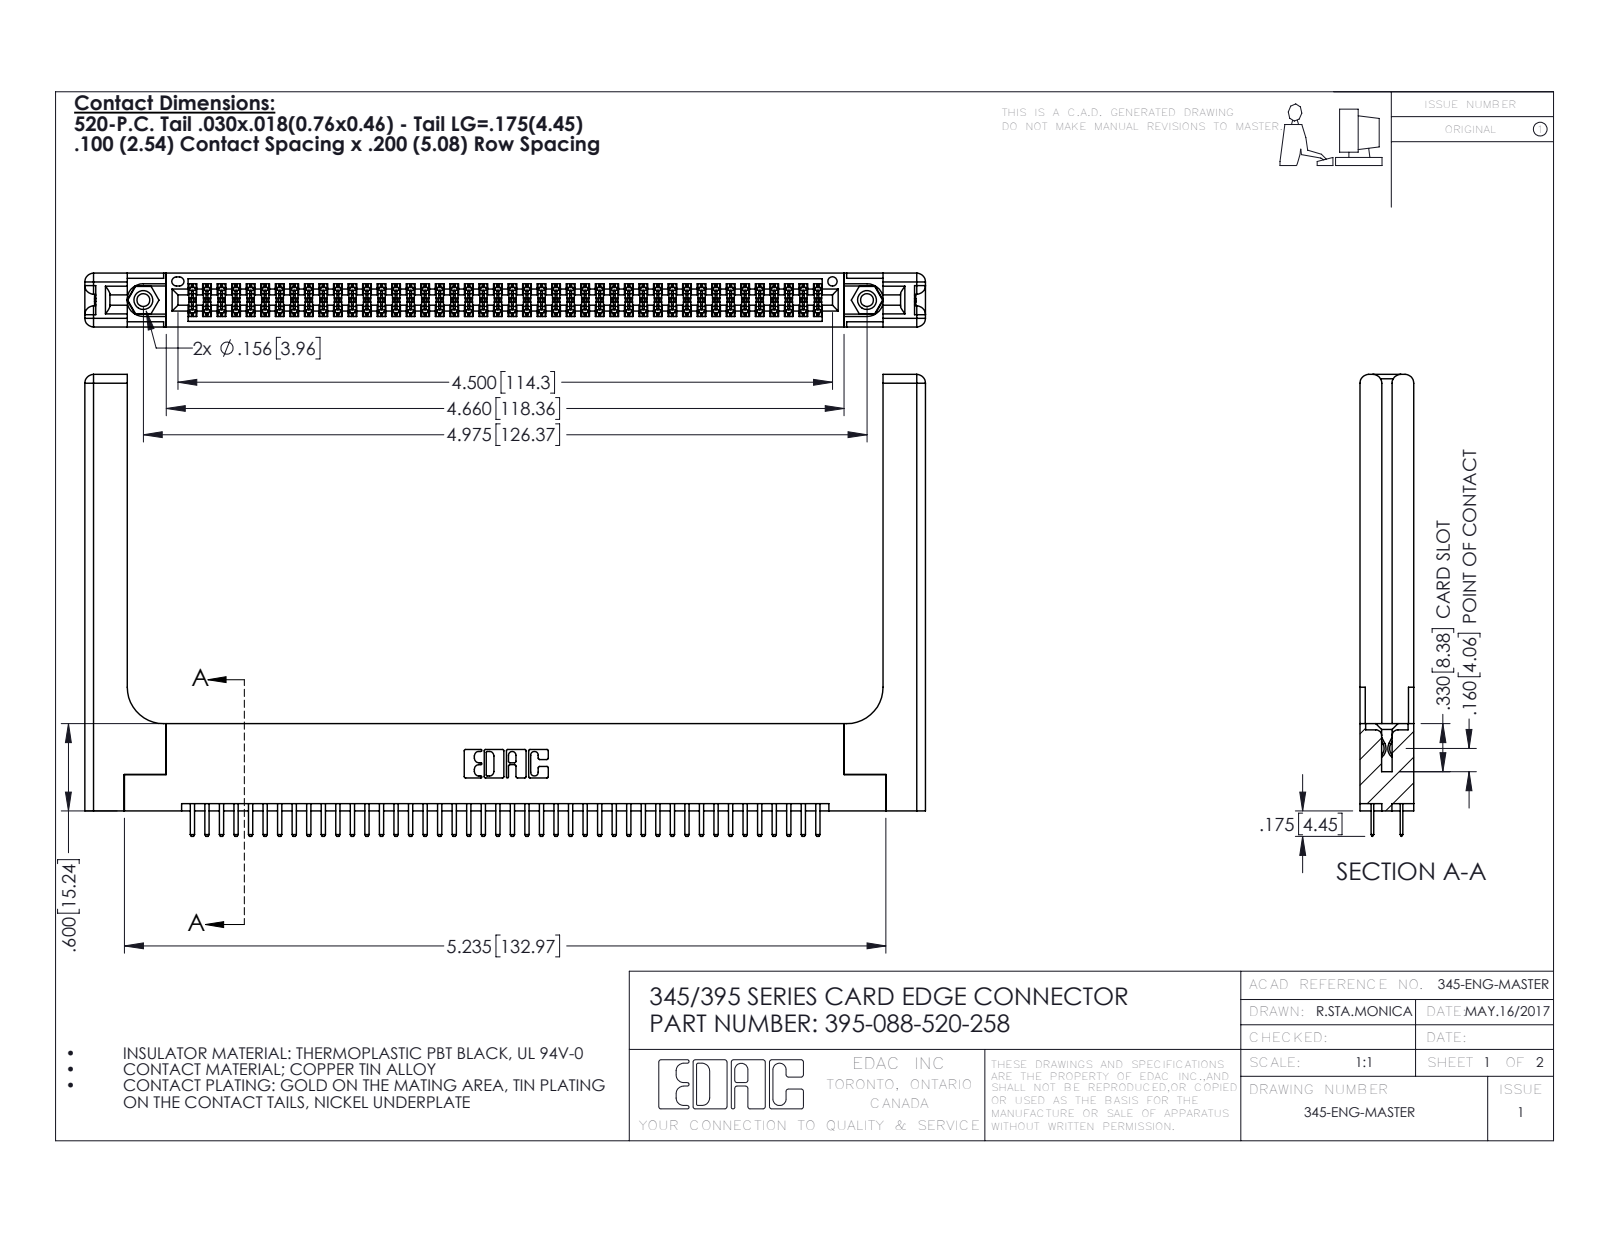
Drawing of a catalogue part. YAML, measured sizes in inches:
part_name: "345-292-001_345-293-120; 345-250-001_345-250-001-102; 395-088-520-258; 345-220-058_345-220-058 (+1 more)"
step_written_by: "SolidWorks 2016 (CONFIG_CONTROL_DESIGN)"
units: inches
bodies: {solids: 93, faces: 5134, planar: 3308, cylindrical: 1766, other: 60}
overall_size: [5.779, 3.175, 0.37]
volume: 1.386
surface_area: 40.4
round_holes:
  - {diameter: 0.089, count: 2}
  - {diameter: 0.125, count: 2}
  - {diameter: 0.156, count: 2}
  - {diameter: 0.064, count: 1}
round_bosses_or_shafts:
  - {diameter: 0.155, count: 2}
partial_cylinders:
  - {radius: 0.006, count: 132}
  - {radius: 0.01, count: 92}
  - {radius: 0.01, count: 22}
  - {radius: 0.06, count: 16}
  - {radius: 0.007, count: 6}
  - {radius: 0.031, count: 6}
  - {radius: 0.026, count: 3}
  - {radius: 0.014, count: 2}
face_to_face_distances: [0.072, 0.37, 0.298, 0.2, 0.098, 0.272, 0.025, 0.225, 0.148, 0.15]
hole_center_spacings: [0.27, 4.739, 4.975]
